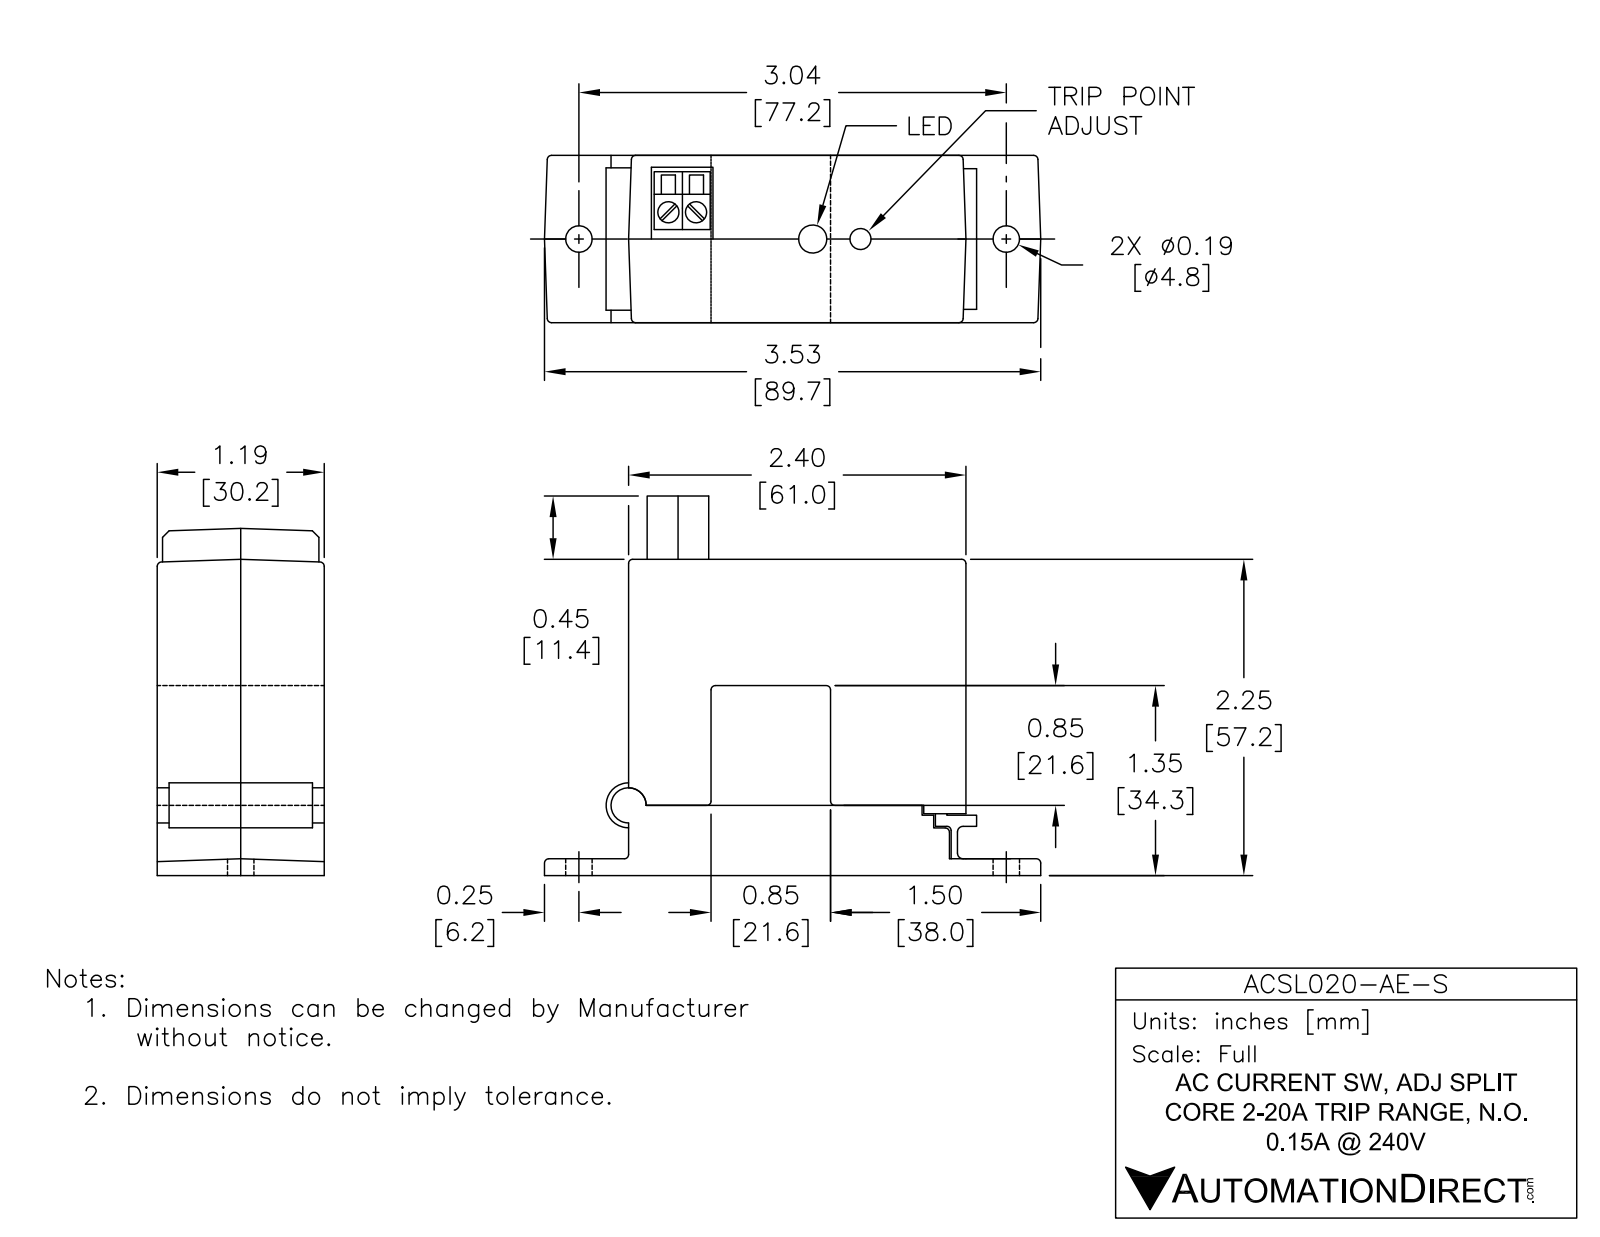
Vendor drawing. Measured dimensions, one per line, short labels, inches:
name: ACSL020-AE-S
written by: SolidWorks 2018 (AUTOMOTIVE_DESIGN)
unit: in
bodies: 8 solids, 475 faces (323 planar, 138 cylindrical, 14 other)
size: 3.53 × 2.743 × 1.2
volume: 5.749 in³; area: 53.51 in²
holes: 2× ⌀0.158, 2× ⌀0.188, 2× ⌀0.2, 1× ⌀0.18
bosses: 2× ⌀0.154, 1× ⌀0.3, 1× ⌀0.25, 1× ⌀0.187, 1× ⌀0.135, 1× ⌀0.063
rounds: 27× R0.016, 2× R0.014, 1× R0.089
face distances: 0.6, 2.258, 1.2, 0.605, 0.595, 0.508, 1.75, 1.75, 2.258, 2.4
hole spacings: 0.171, 0.345, 0.606, 0.772, 0.835, 1.002, 1.102, 1.174
